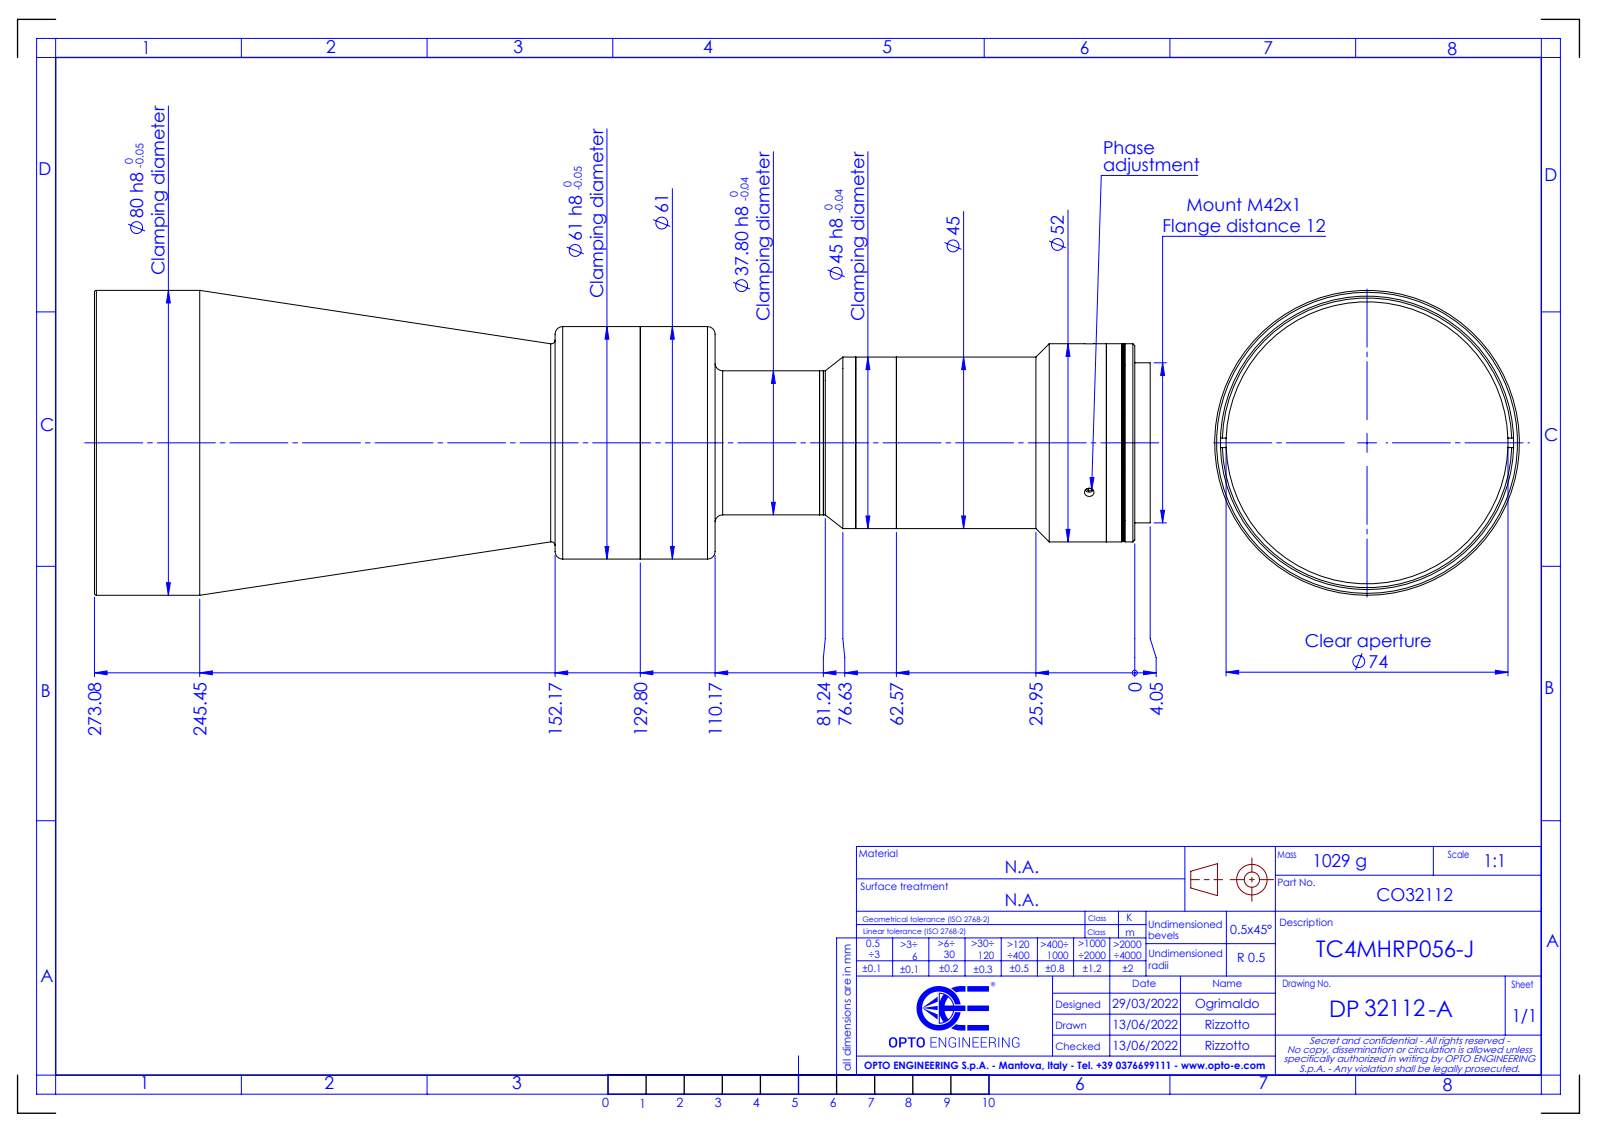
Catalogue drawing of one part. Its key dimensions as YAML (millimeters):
part_name: "DP32112-A_TC4MHRP056-J"
step_written_by: "SolidWorks 2021 (CONFIG_CONTROL_DESIGN)"
units: millimeters
bodies: {solids: 0, faces: 100, planar: 20, cylindrical: 52, other: 28}
overall_size: [277.12, 80, 80]
round_holes:
  - {diameter: 2.5, count: 3}
  - {diameter: 38, count: 1}
  - {diameter: 41, count: 1}
  - {diameter: 53, count: 1}
  - {diameter: 74, count: 1}
  - {diameter: 77, count: 1}
round_bosses_or_shafts:
  - {diameter: 80, count: 1}
  - {diameter: 61, count: 1}
  - {diameter: 52, count: 1}
  - {diameter: 51.8, count: 1}
  - {diameter: 45, count: 1}
  - {diameter: 42, count: 1}
  - {diameter: 37.8, count: 1}
face_to_face_distances: [107.62, 106.73, 0.89, 110.18, 3.45, 2.56, 102.73, 4, 4.89, 7.45]
